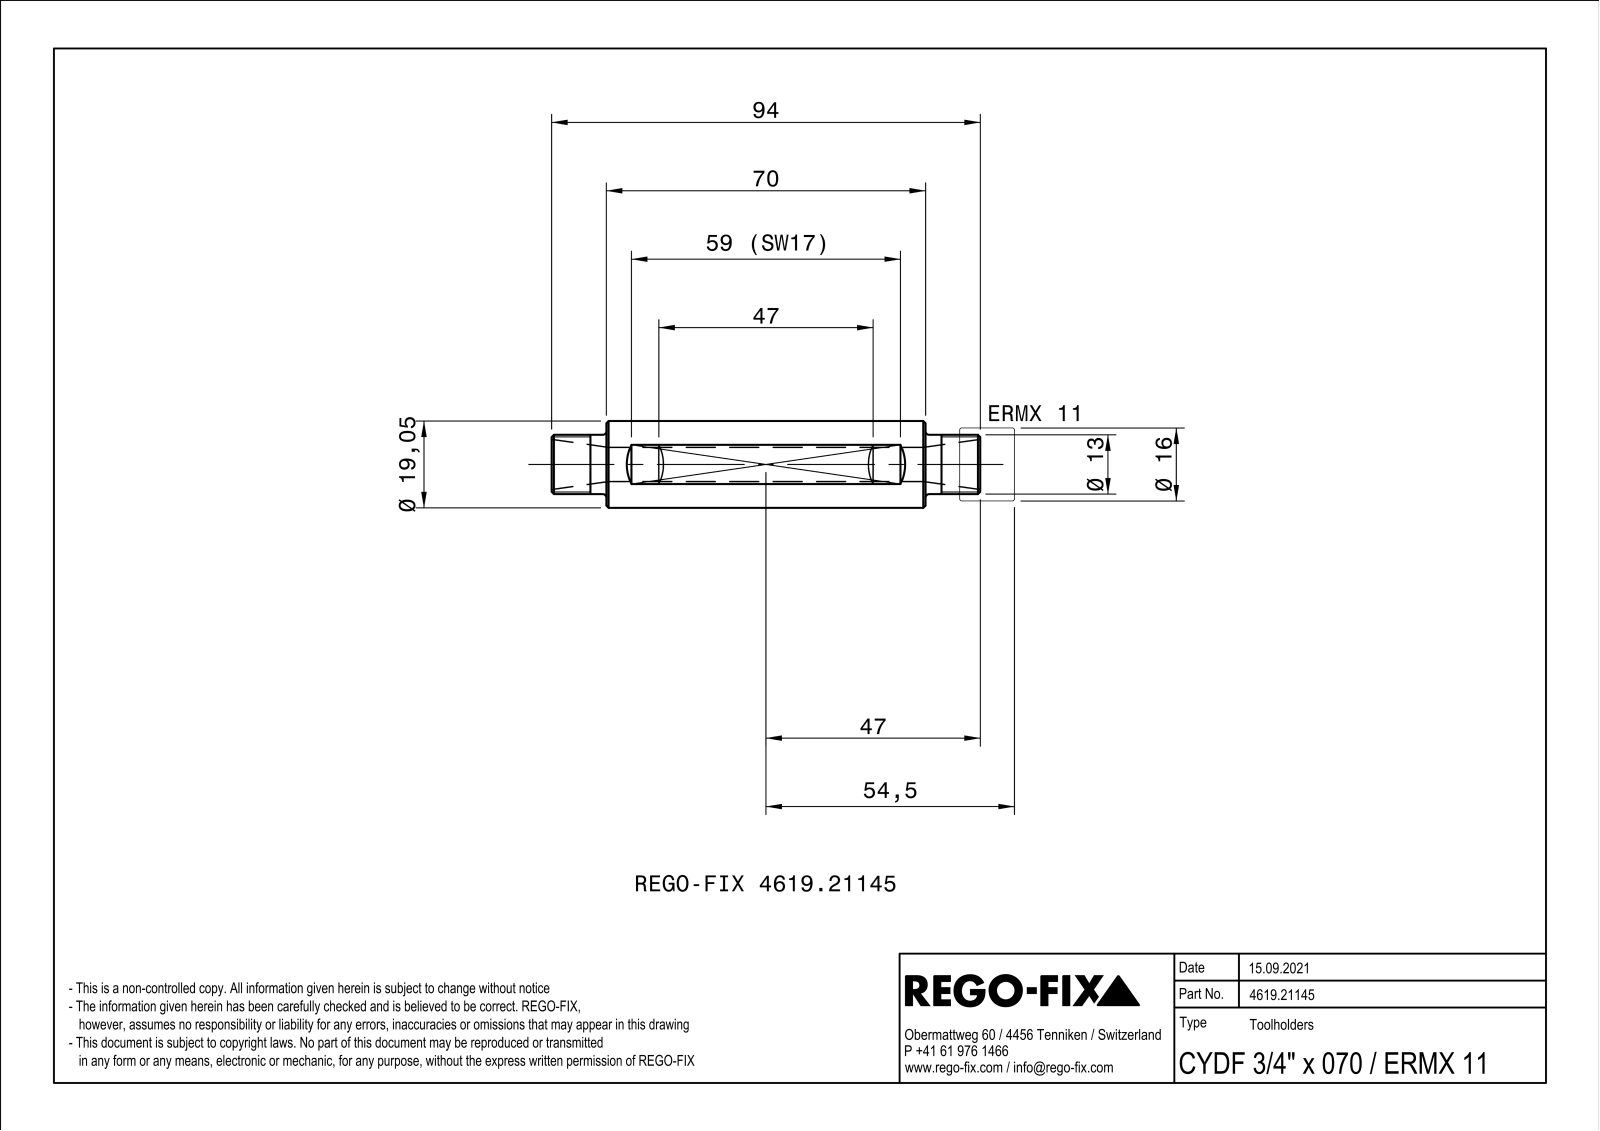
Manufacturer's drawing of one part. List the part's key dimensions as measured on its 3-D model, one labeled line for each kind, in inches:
Part name (STEP PRODUCT): NOCUT
STEP written by: SIEMENS PLM Software Solid Edge ST10 (AUTOMOTIVE_DESIGN)
Units: inches
Bodies: 1 solid, 29 faces (13 planar, 6 cylindrical, 10 other)
Overall size (bounding box): 3.701 × 0.75 × 0.75
Volume: 1.095 in³ · Surface area: 12.1 in²
Round holes (diameter × count): ⌀0.295 ×1
Round bosses / shafts (diameter × count): ⌀0.75 ×1, ⌀0.512 ×1
Main face-to-face distances: 0.669, 2.756, 0.472, 3.228, 1.169, 0.306, 1.475, 3.701
